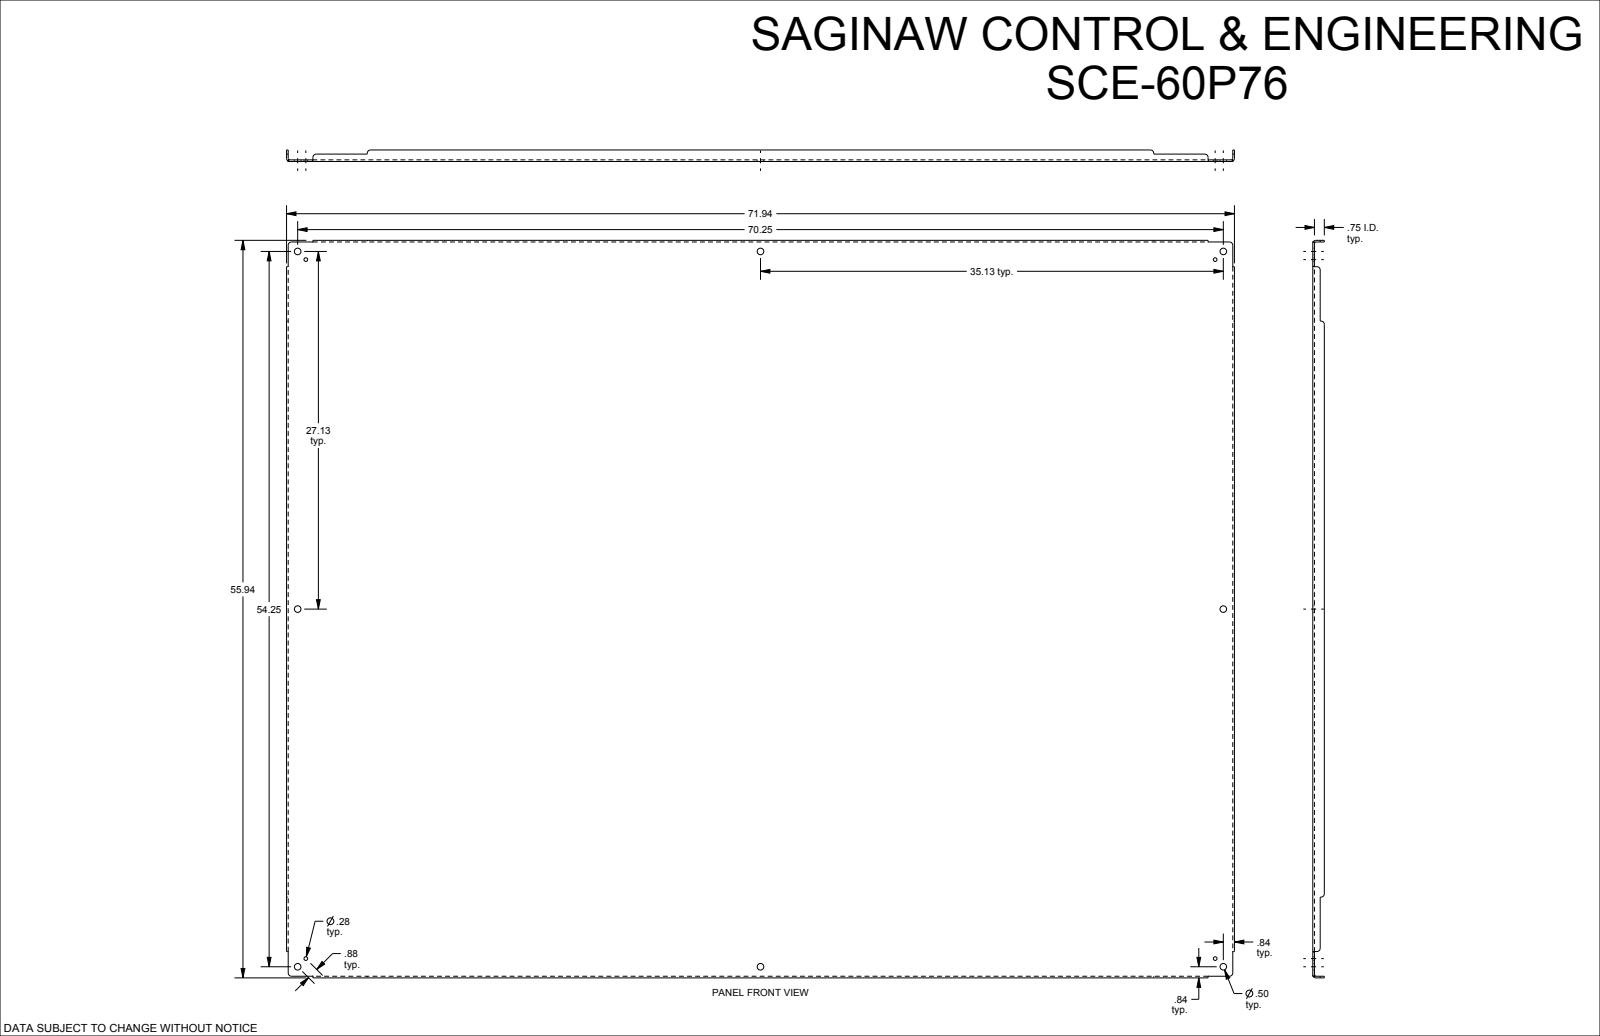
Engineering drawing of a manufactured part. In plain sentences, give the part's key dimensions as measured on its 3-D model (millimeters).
The part is named "SCE-60P76". Its 3-D file was written by "SolidWorks 2019 (CONFIG_CONTROL_DESIGN)". It is 1 solid with 110 faces: 46 planar, 40 cylindrical and 24 other. Overall it measures 1827.2 by 1420.8 by 22.2 millimeters. Its volume is 8 544 000 cubic millimeters and its surface area 5 405 000 square millimeters. Round holes: 8 of diameter 12.7, 4 of diameter 7.1. Partial cylindrical surfaces (rounded edges, fillets, slot ends): 12 of radius 6.4, 4 of radius 2.8, 4 of radius 6. The main face-to-face distances are 3.2, 3.2, 1417.7, 1824.1, 1414.4, 1420.8, 1820.8, 1827.2, 19.1, 22.2. The hole center spacings are 22.2, 673.4, 689, 876.6, 892.2, 1127.2, 1362.3, 1619.8.
